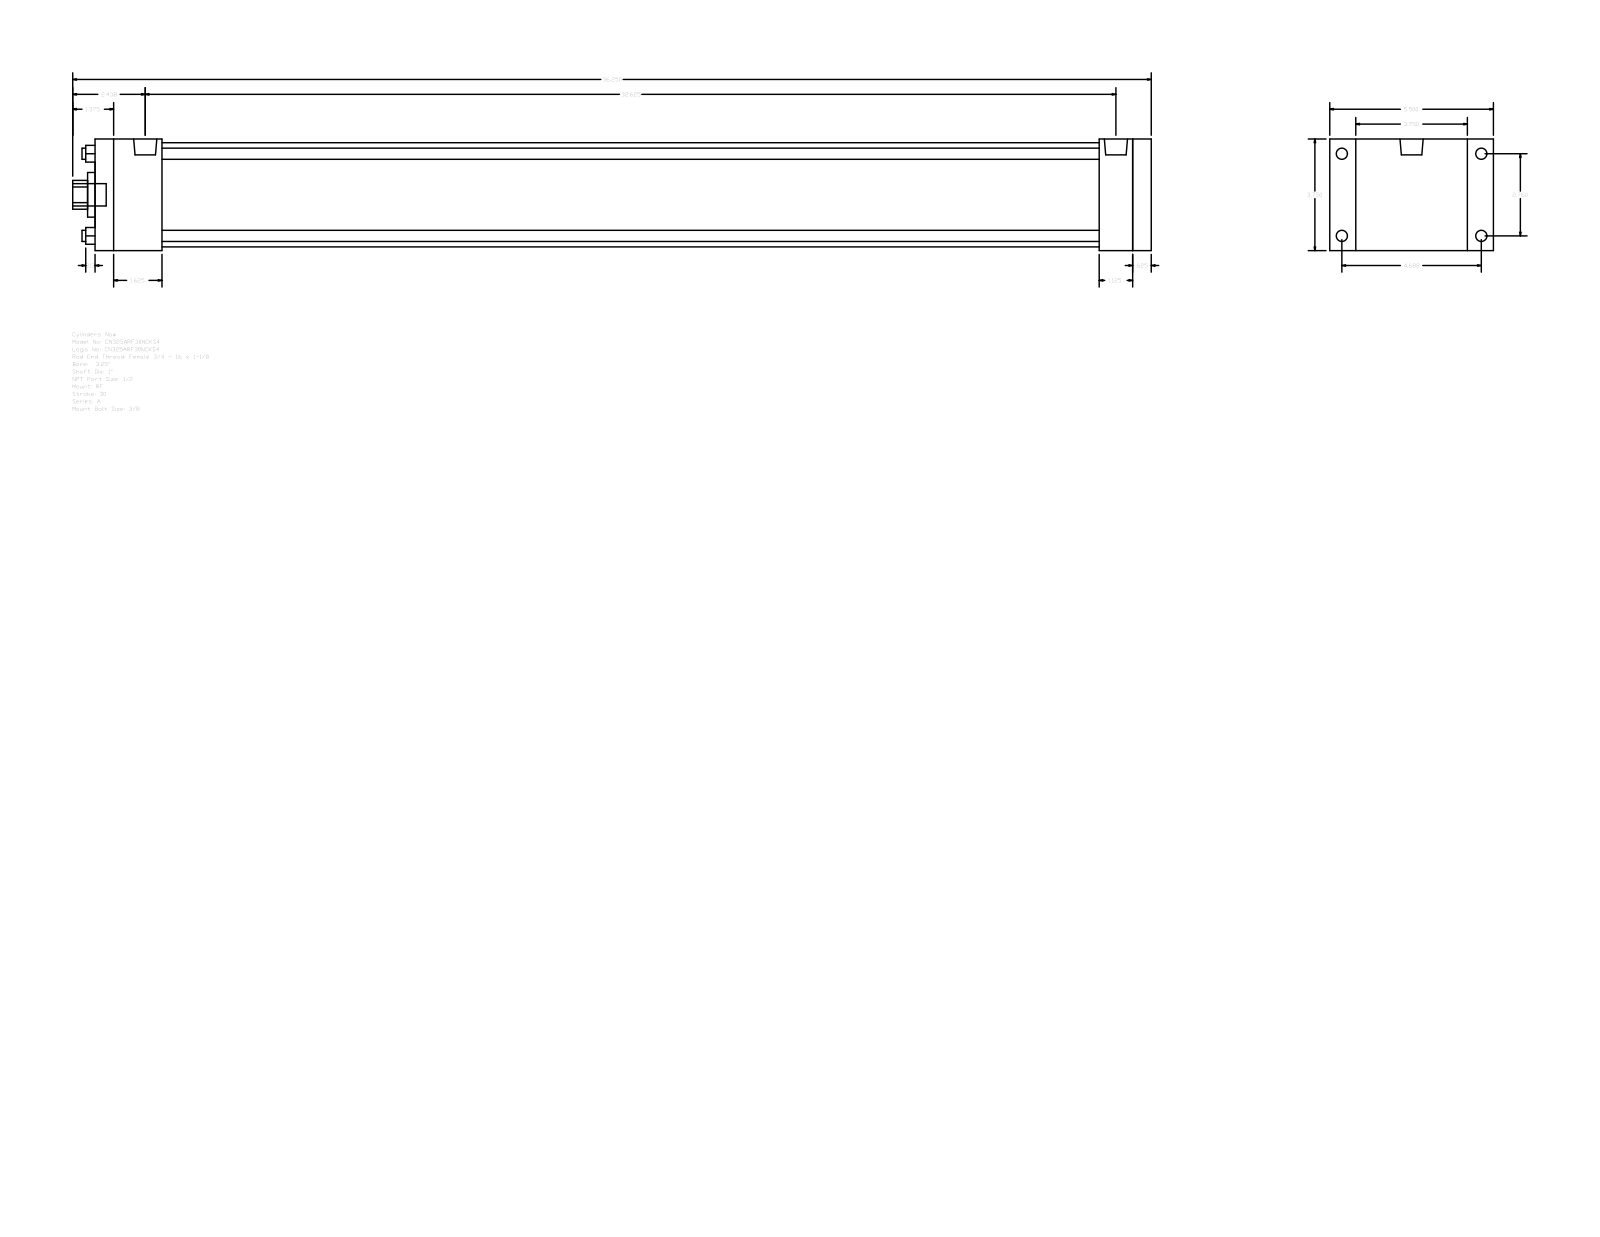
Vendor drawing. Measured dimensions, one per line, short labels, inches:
name: A_RF__0325_1
written by: GSSL Pune (CONFIG_CONTROL_DESIGN)
unit: in
bodies: 0 solids, 92 faces (64 planar, 28 cylindrical, 0 other)
size: 36.25 × 5.5 × 3.75
holes: 4× ⌀0.375, 1× ⌀1, 1× ⌀1.5, 1× ⌀3.5
bosses: 4× ⌀0.375, 4× ⌀0.344, 2× ⌀0.778, 1× ⌀0.75
rounds: 1× R0.484
face distances: 3.75, 35.5, 0.625, 34.875, 0.875, 4.625, 33.75, 1.125, 1.75, 2.25
hole spacings: 1.952, 2.76, 3.903
